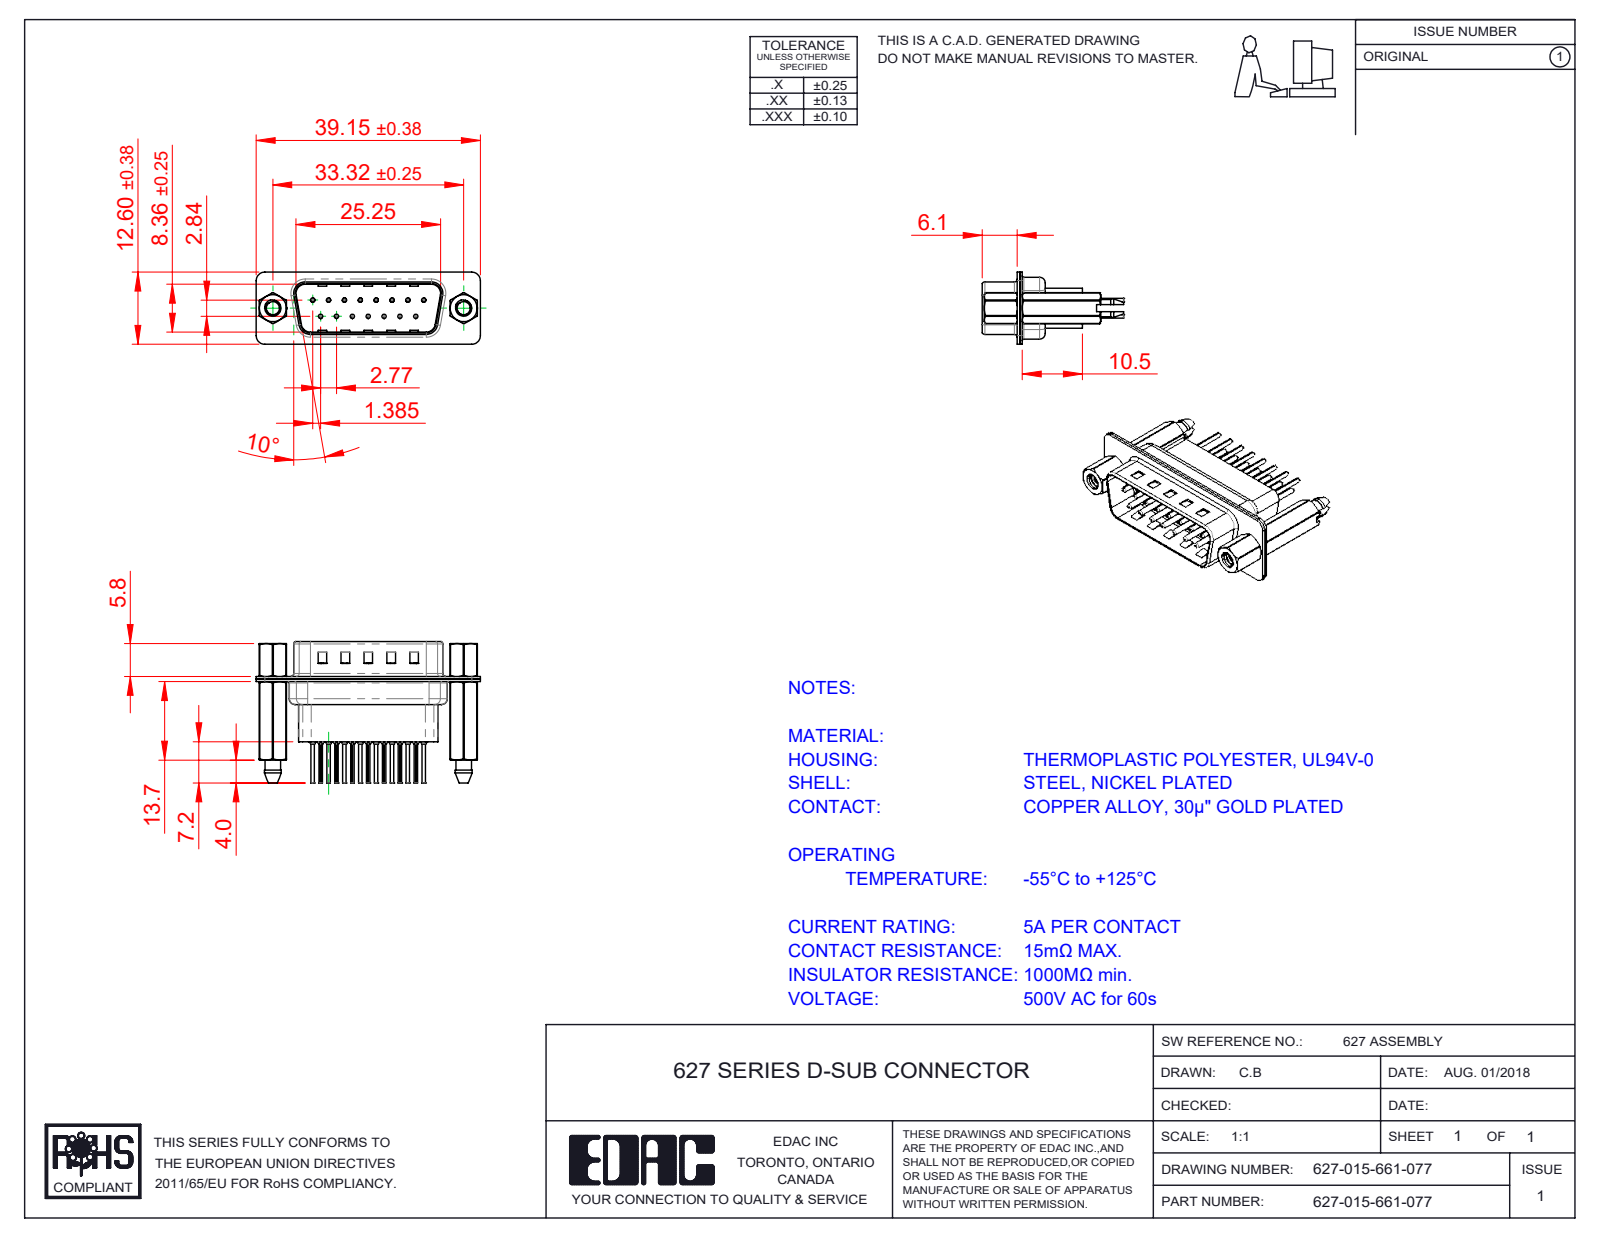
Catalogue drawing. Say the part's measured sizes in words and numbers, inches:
The part is named "627 Contact Row 1_61; 627-015-661-077; 627 Shell Rear_15 Contacts; 627 Contact Row 2_61 (+4 more)". Its 3-D file was written by "SolidWorks 2020 (CONFIG_CONTROL_DESIGN)". It is 22 solids with 2044 faces: 553 planar, 826 cylindrical and 665 other. Overall it measures 1.541 by 0.969 by 0.496 inches. Its volume is 0.19 cubic inches and its surface area 12.36 square inches. Round holes: 15 of diameter 0.008, 15 of diameter 0.014, 15 of diameter 0.043, 15 of diameter 0.063, 2 of diameter 0.089, 2 of diameter 0.09, 2 of diameter 0.157, 2 of diameter 0.189. Round bosses or shafts: 15 of diameter 0.079, 15 of diameter 0.059, 15 of diameter 0.03, 15 of diameter 0.024, 2 of diameter 0.193, 2 of diameter 0.11. Partial cylindrical surfaces (rounded edges, fillets, slot ends): 30 of radius 0.004, 18 of radius 0.059, 12 of radius 0.079, 10 of radius 0.063, 8 of radius 0.02, 4 of radius 0.01, 4 of radius 0.024, 4 of radius 0.026. The main face-to-face distances are 0.016, 0.018, 0.187, 0.035, 0.032, 0.377, 0.059, 0.027, 0.302, 0.656. The hole center spacings are 0.124, 0.109, 0.218, 0.327, 0.436, 0.198, 0.198, 0.294.
